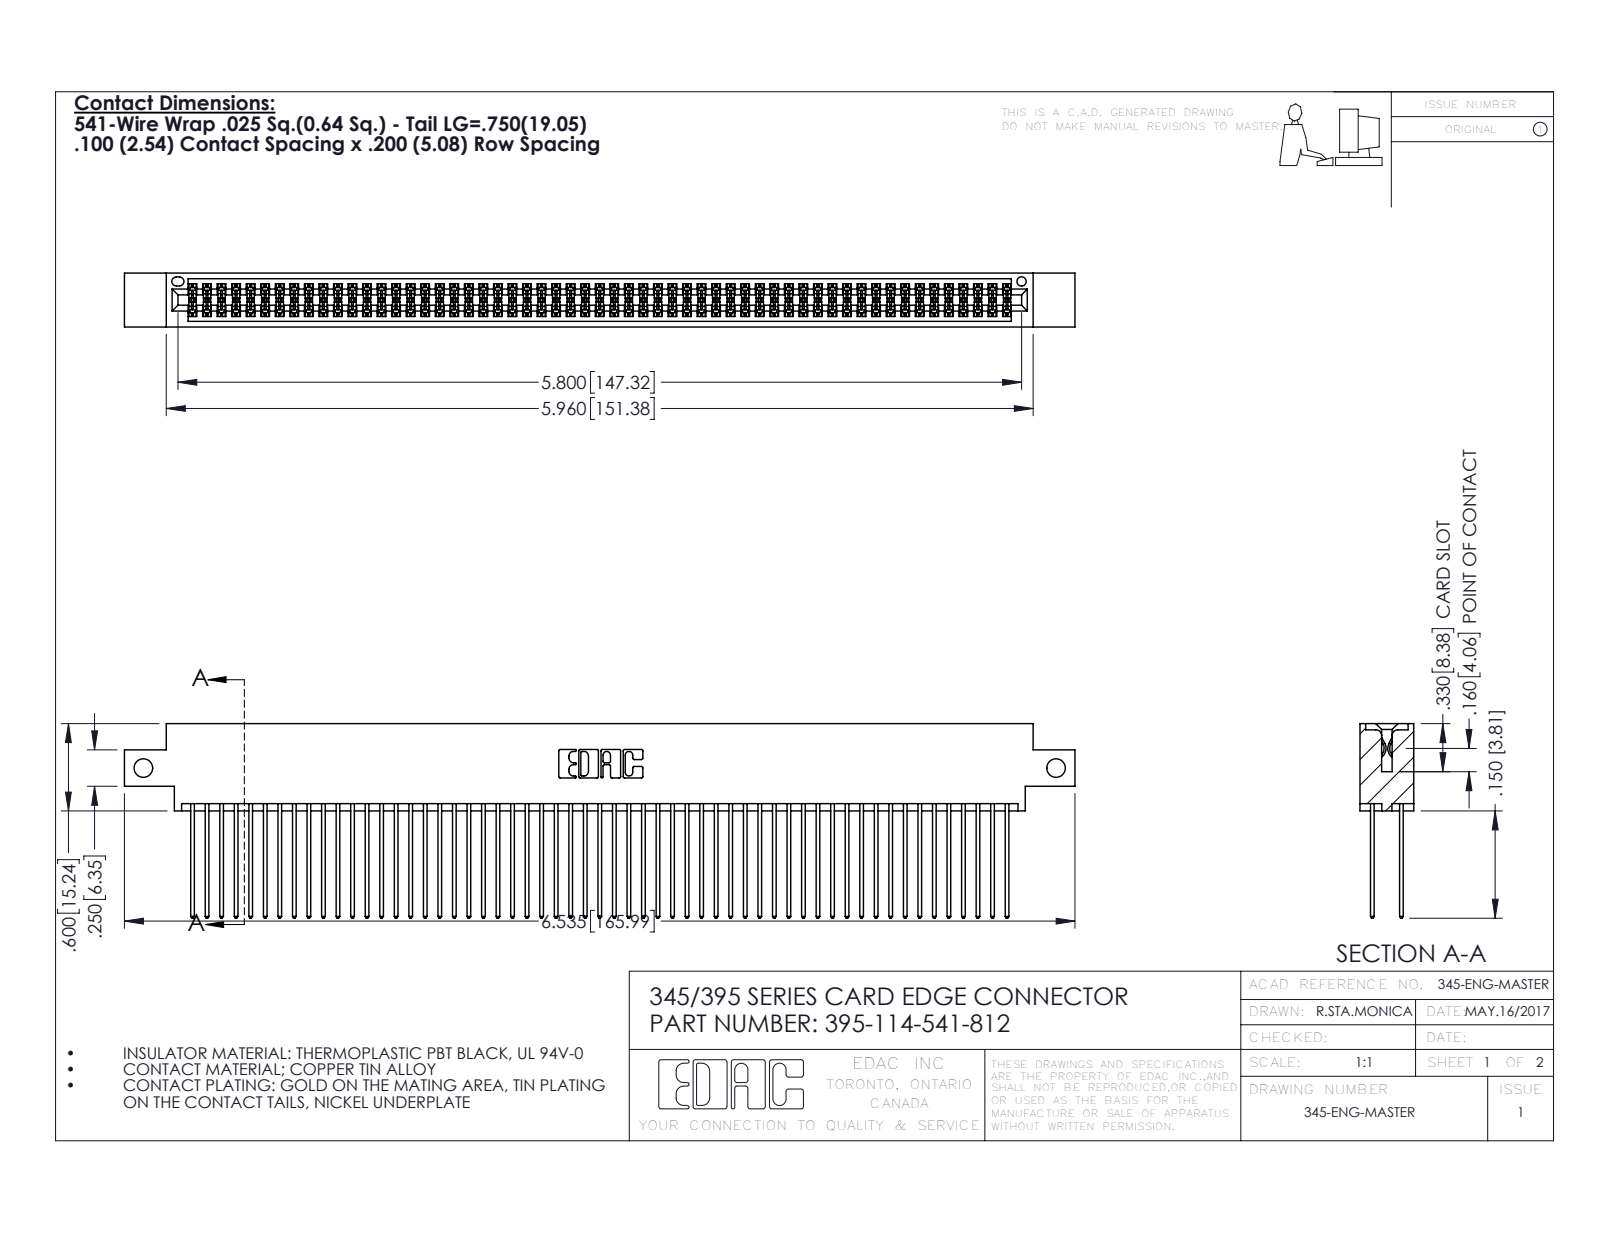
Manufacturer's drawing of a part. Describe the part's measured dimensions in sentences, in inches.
The part is named "345 Part_0.170 Offset - Side Mount; 395-114-541-812; 345-292-001_345-293-141". Its 3-D file was written by "SolidWorks 2016 (CONFIG_CONTROL_DESIGN)". It is 115 solids with 5830 faces: 3846 planar, 1984 cylindrical and 0 other. Overall it measures 6.535 by 1.337 by 0.37 inches. Its volume is 1.02 cubic inches and its surface area 43.53 square inches. Round holes: 2 of diameter 0.128, 1 of diameter 0.064. Partial cylindrical surfaces (rounded edges, fillets, slot ends): 171 of radius 0.006, 114 of radius 0.01, 22 of radius 0.01, 6 of radius 0.007, 6 of radius 0.031, 3 of radius 0.026, 2 of radius 0.014, 2 of radius 0.019. The main face-to-face distances are 0.072, 0.298, 0.2, 0.098, 0.272, 0.025, 0.225, 0.37, 0.175, 0.149. The hole center spacings are 6.275.
